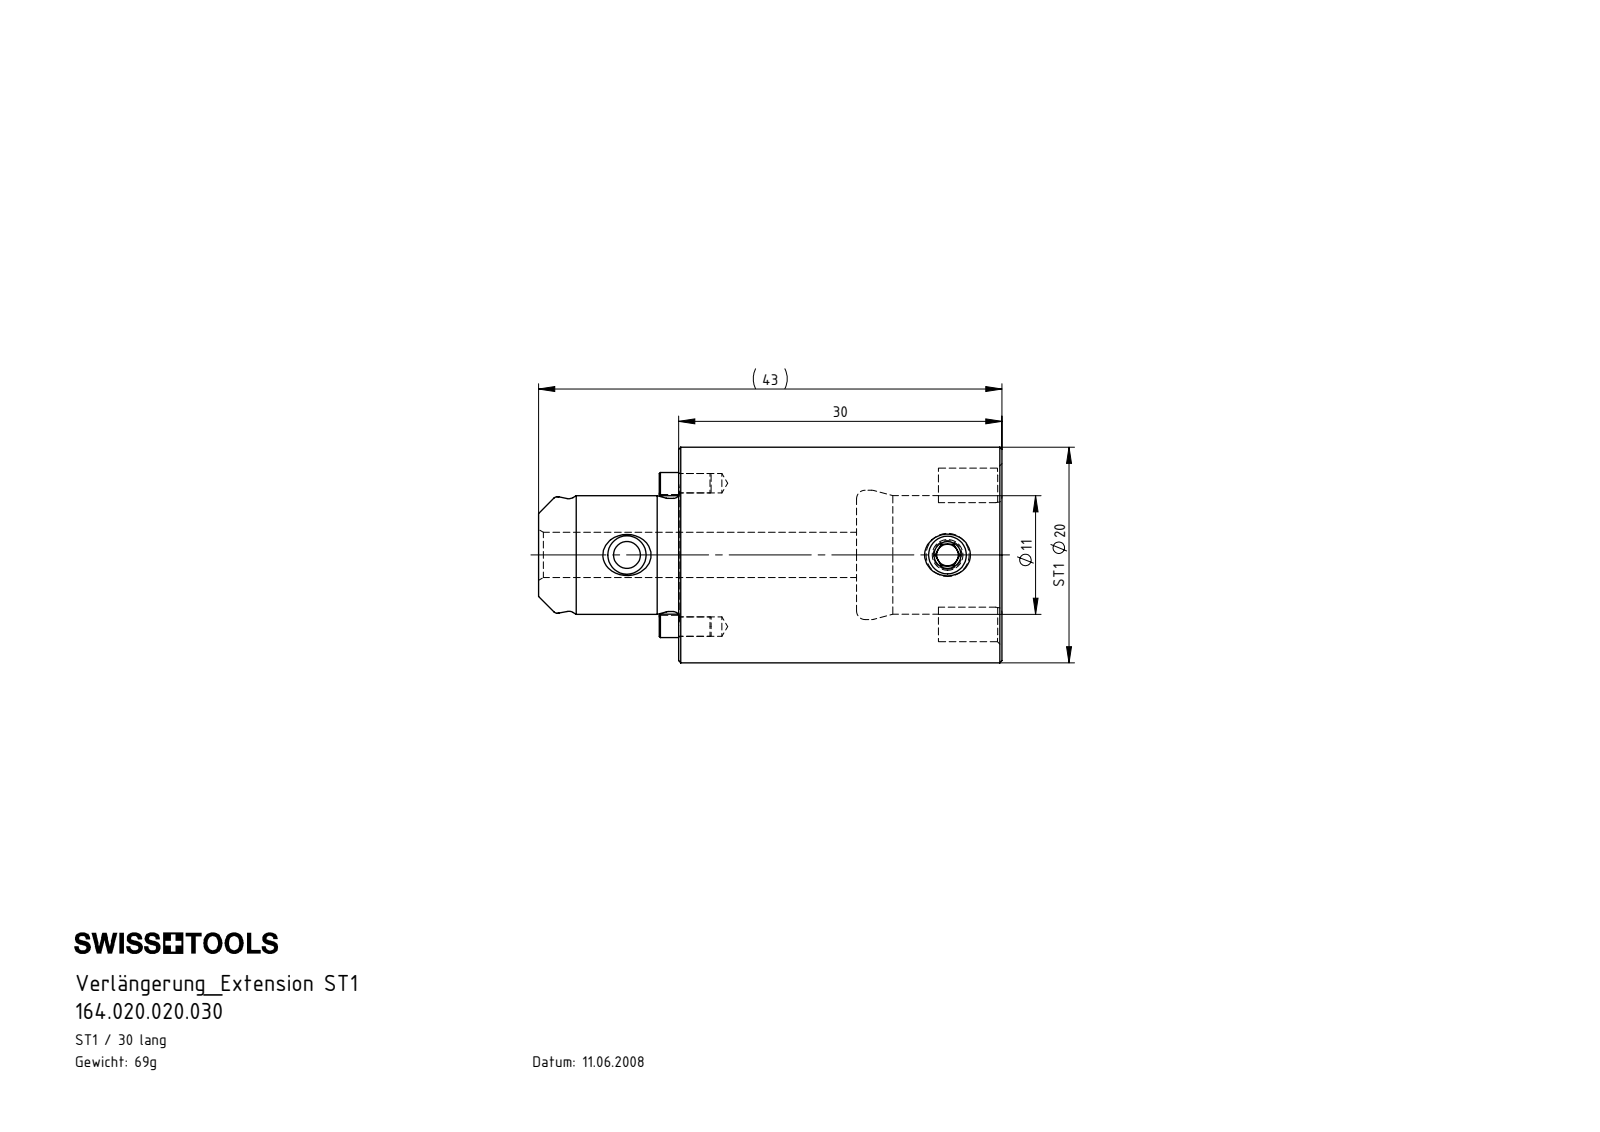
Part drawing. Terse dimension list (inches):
name: ST1-ER2.001.005_A; ST1-ST1.K01.030_A; ST1-ER1.001.005_A; ST1-ST1.K01.030
written by: SolidWorks 2015 (CONFIG_CONTROL_DESIGN)
unit: in
bodies: 4 solids, 146 faces (26 planar, 43 cylindrical, 77 other)
size: 1.693 × 0.787 × 0.787
volume: 0.534 in³; area: 6.268 in²
holes: 2× ⌀0.071, 1× ⌀0.098, 1× ⌀0.138, 1× ⌀0.165, 1× ⌀0.433, 1× ⌀0.472
bosses: 1× ⌀0.787, 1× ⌀0.425, 1× ⌀0.413, 1× ⌀0.157
rounds: 4× R0.012, 2× R0.051, 2× R0.058, 2× R0.219
face distances: 1.181, 0.531, 0.65, 0.368, 0.512, 1.161, 1.693, 1.461, 0.949, 0.299
hole spacings: 0.262, 0.524, 1.171
